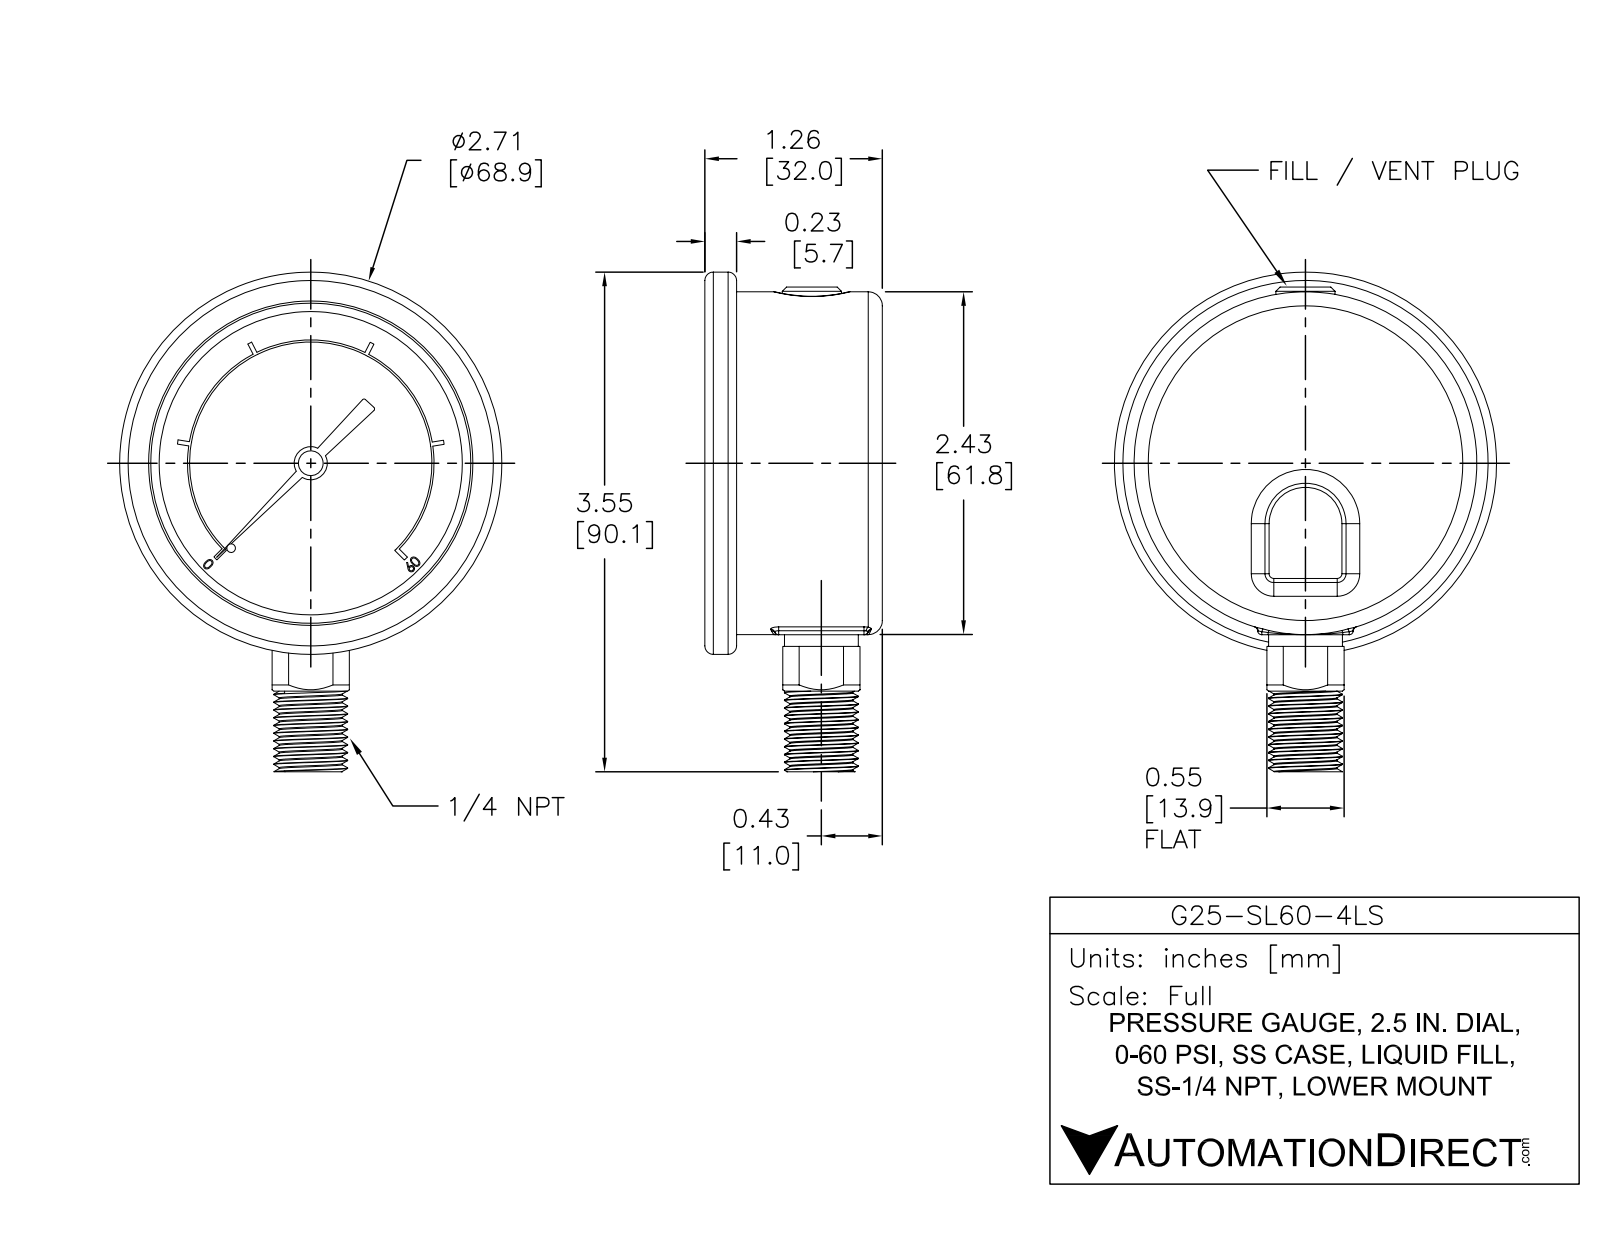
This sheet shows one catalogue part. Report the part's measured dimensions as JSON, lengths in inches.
{"part_name": "G25-SL60-4LS", "step_written_by": "SolidWorks 2021 (AUTOMOTIVE_DESIGN)", "units": "inches", "bodies": {"solids": 1, "faces": 339, "planar": 191, "cylindrical": 85, "other": 63}, "overall_size": [3.546, 2.713, 1.26], "volume_in3": 5.273, "surface_area_in2": 24.67, "round_holes": [[0.027, 1], [0.071, 1], [0.119, 1], [2.272, 1]], "round_bosses_or_shafts": [[2.713, 1], [2.433, 1], [0.524, 1], [0.42, 1], [0.235, 1], [0.176, 1], [0.14, 1], [0.041, 1]], "partial_cylinders_radius": [[0.03, 9], [0.1, 3], [0.015, 2], [0.316, 1], [0.86, 1], [0.875, 1]], "face_to_face_distances": [1.01, 1.26, 0.25, 1.035, 0.025, 0.225, 0.1, 0.91, 0.935, 1.16], "hole_center_spacings": [0.067]}
